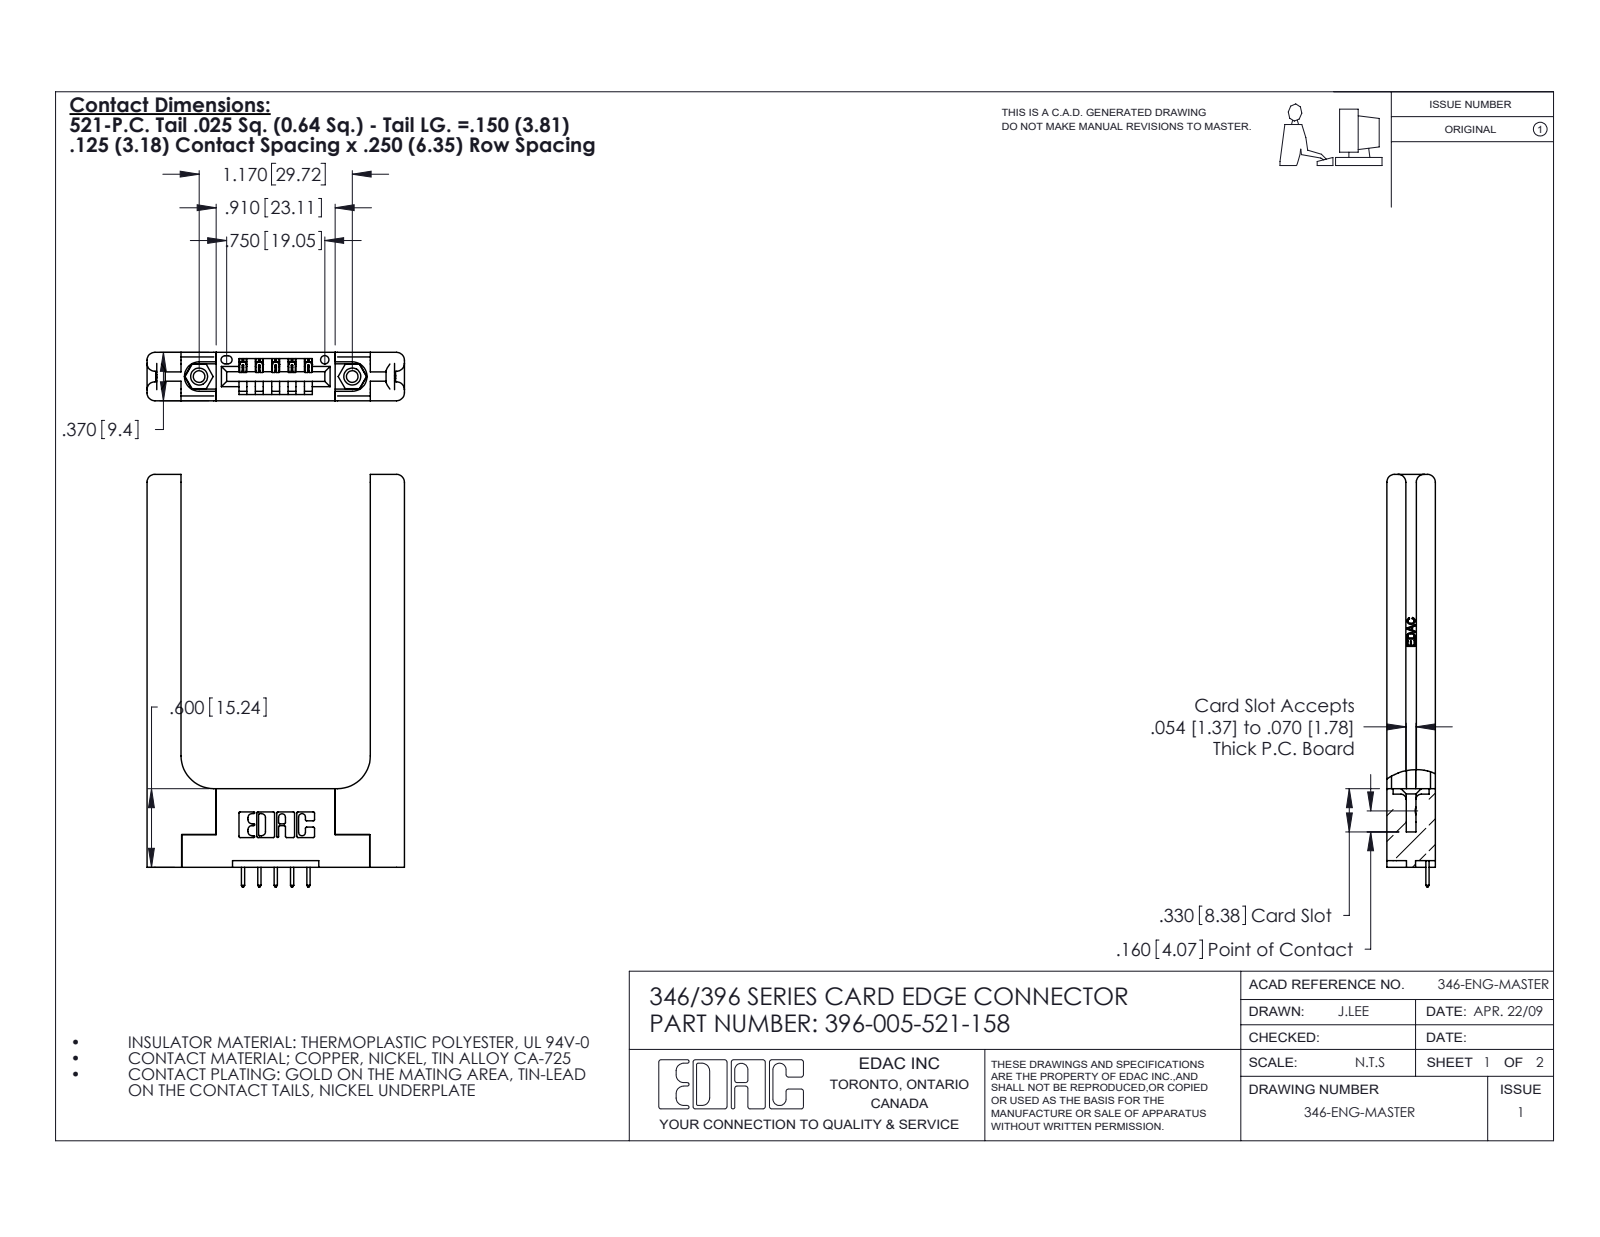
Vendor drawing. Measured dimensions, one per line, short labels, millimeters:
name: 346-220-058_345-220-058; 346 Part_Flush Mounting Lugs - 0.156 Dia-TH; 345-292-001_345-293-121; 396-005-521-158 (+1 more)
written by: SolidWorks 2020 (CONFIG_CONTROL_DESIGN)
unit: mm
bodies: 10 solids, 682 faces (438 planar, 184 cylindrical, 60 other)
size: 80 × 49.9 × 9.4
volume: 12 000 mm³; area: 10 360 mm²
holes: 2× ⌀2.3, 2× ⌀3.2, 2× ⌀4, 1× ⌀1.6
bosses: 2× ⌀3.9
rounds: 22× R0.3, 16× R1.5, 10× R0.2, 10× R0.3, 6× R0.2, 6× R0.8, 3× R0.7, 2× R0.8
face distances: 9.4, 3.8, 5.6, 6.4, 1.8, 36.7, 3.8, 1.8, 6.6, 43.3
hole spacings: 6.2, 24.6, 29.7
